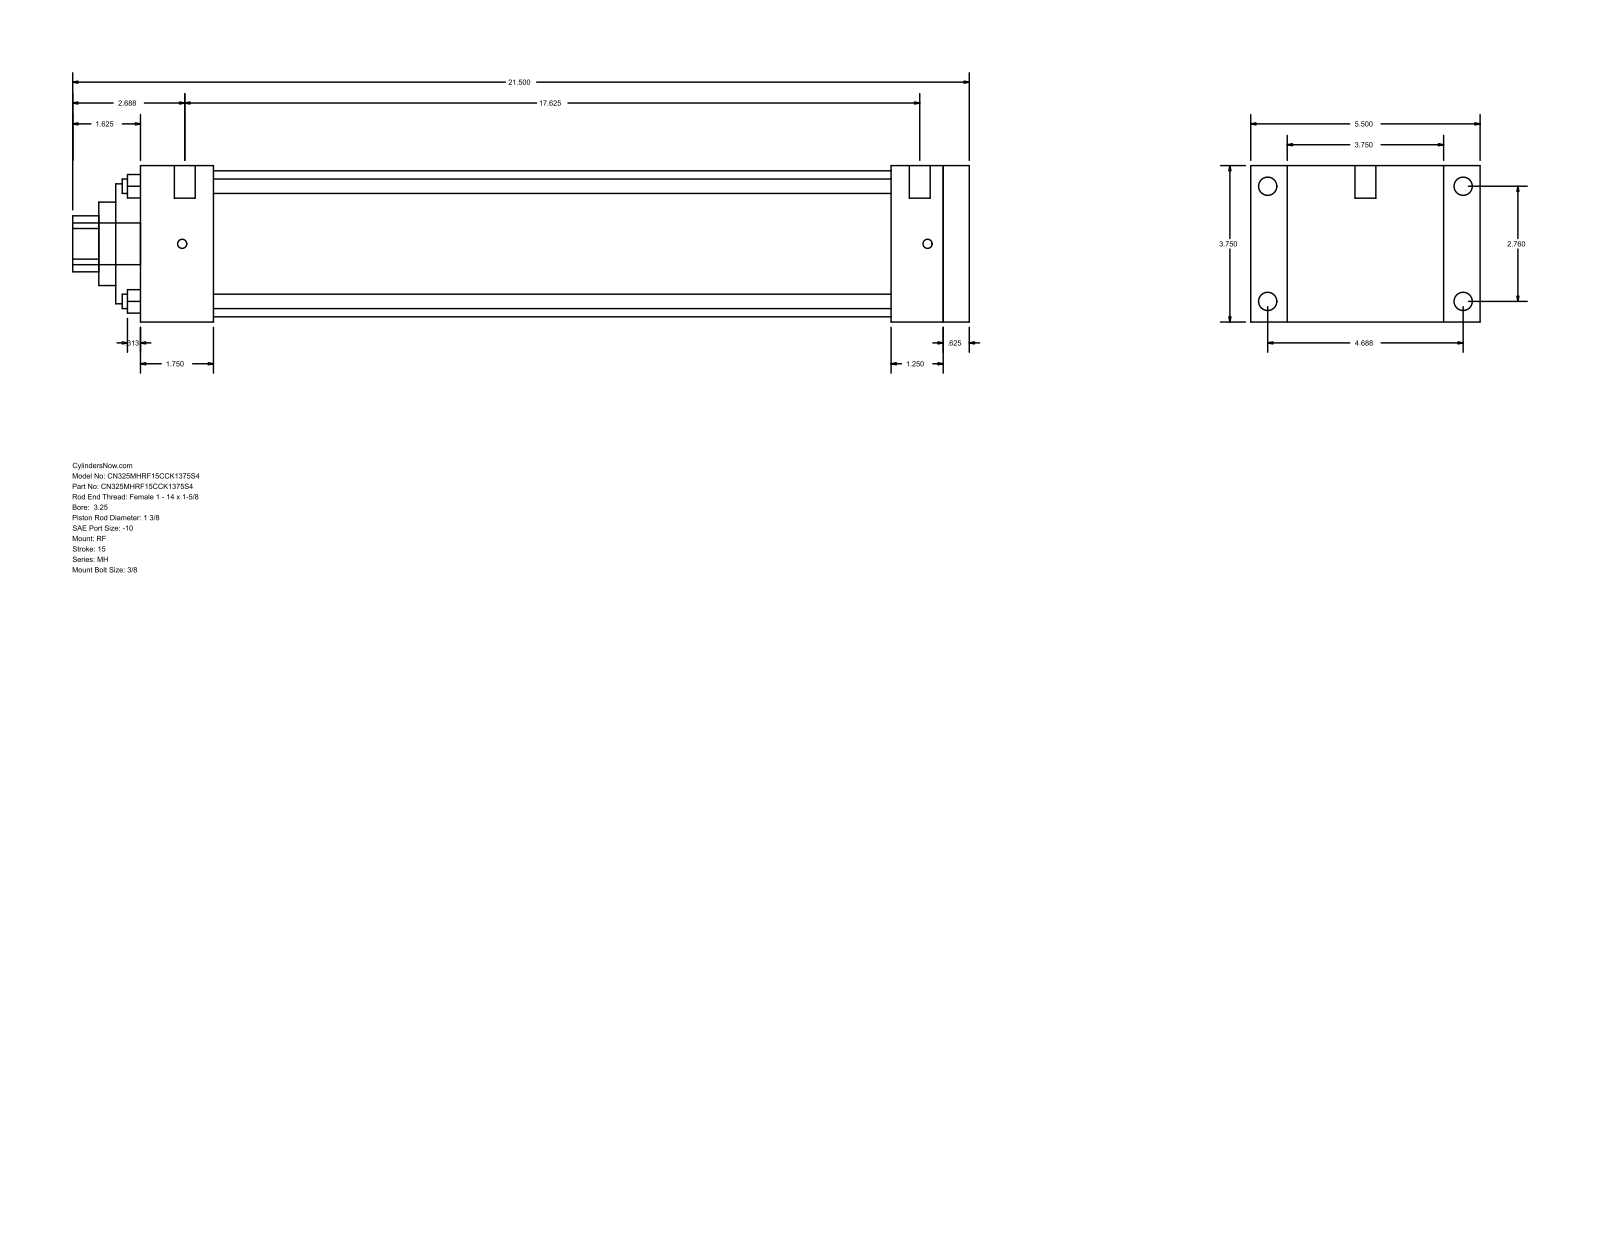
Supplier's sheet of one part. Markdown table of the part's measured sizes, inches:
| quantity | value |
| --- | --- |
| part name | MH_RF__0325_1.375 |
| STEP written by | GSSL Pune (CONFIG_CONTROL_DESIGN) |
| units | inches |
| bodies | 0 solids, 94 faces (65 planar, 29 cylindrical, 0 other) |
| overall size | 21.5 × 5.5 × 3.75 |
| round holes (diameter × count) | 0.345 × 4, 1.375 × 1, 2 × 1, 2.875 × 1, 3.5 × 1 |
| round bosses / shafts (diameter × count) | 0.438 × 4, 0.219 × 4, 0.5 × 2, 1 × 1 |
| partial cylindrical surfaces (radius × count) | 0.672 × 1 |
| main face-to-face distances | 3.75, 19.875, 19.25, 0.625, 0.875, 4.625, 1.75, 17.5, 18.125, 18 |
| hole center spacings | 1.952, 2.76, 3.903 |
